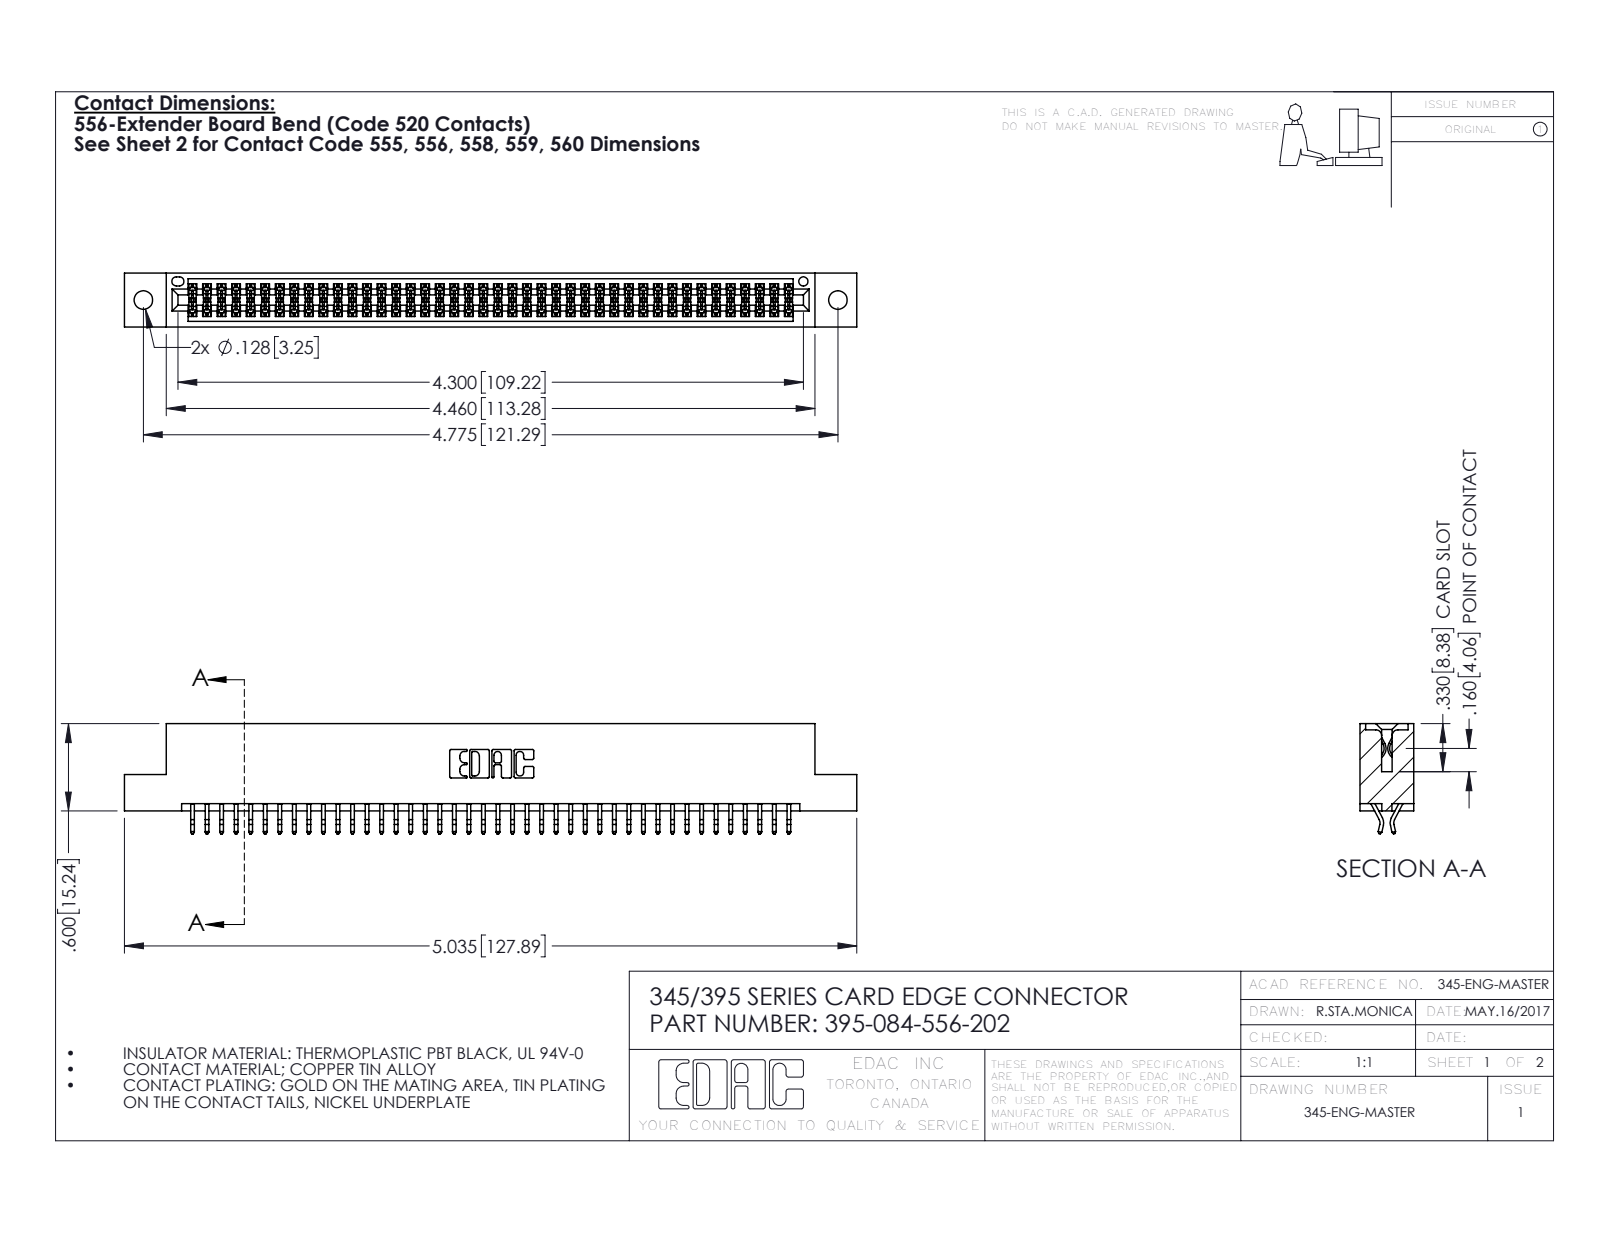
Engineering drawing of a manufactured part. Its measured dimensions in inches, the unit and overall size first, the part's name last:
Units: inches
Overall size (bounding box): 5.035 × 0.757 × 0.37
Round holes (diameter × count): ⌀0.128 ×2, ⌀0.064 ×1
Partial cylindrical surfaces — rounded edges, fillets, slot ends (radius × count): R0.006 ×126, R0.01 ×22, R0.007 ×6, R0.031 ×6, R0.026 ×3, R0.01 ×2, R0.014 ×2, R0.019 ×2
Main face-to-face distances: 0.298, 0.072, 0.2, 0.37, 0.025, 0.098, 0.272, 0.225, 0.175, 0.149
Hole centre spacings: 0.27, 4.539, 4.775
Volume: 0.756 in³ · Surface area: 27.84 in²
Bodies: 85 solids, 4830 faces (3188 planar, 1642 cylindrical, 0 other)
Part name (STEP PRODUCT): 395-084-556-202; 345 Part_Flush Mounting Lugs - 0.128 Dia; 345-292-001_556 Tail
STEP written by: SolidWorks 2016 (CONFIG_CONTROL_DESIGN)
